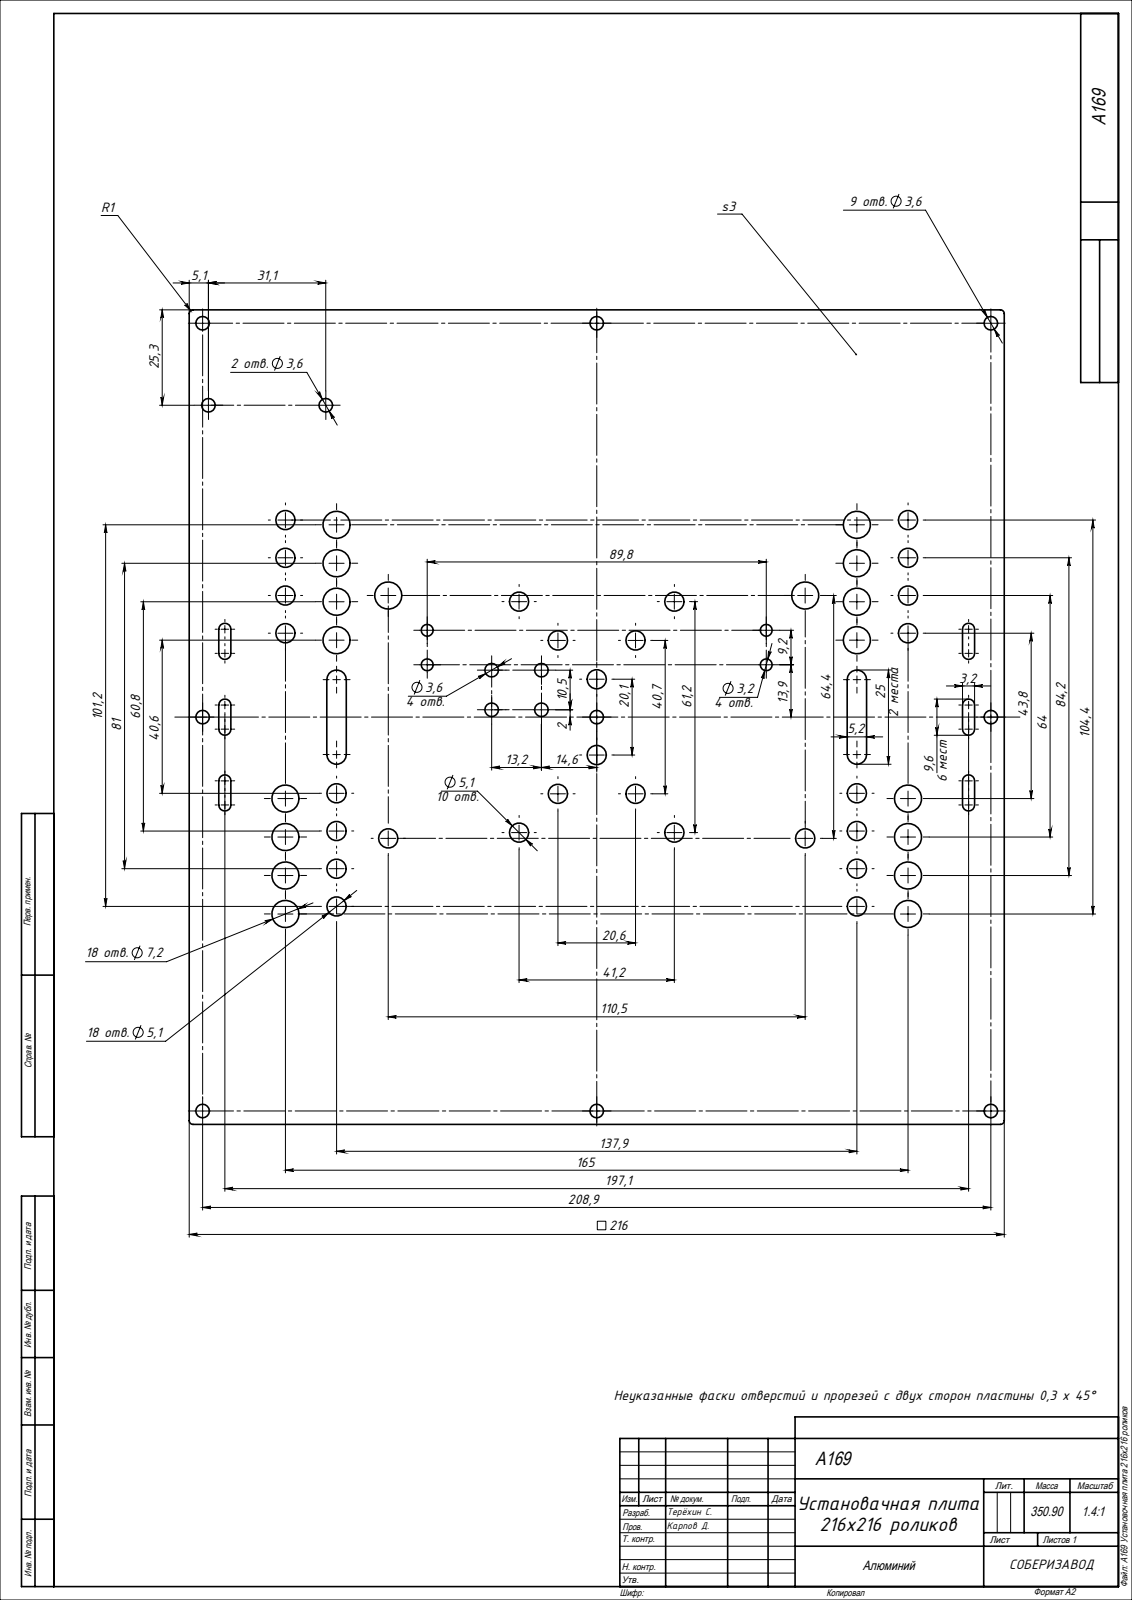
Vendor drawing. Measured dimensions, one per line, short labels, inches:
name: A169 Установочная плита 216х216 роликов
written by: SolidWorks 2019 (AUTOMOTIVE_DESIGN)
unit: in
bodies: 1 solid, 172 faces (22 planar, 150 cylindrical, 0 other)
size: 8.504 × 8.504 × 0.118
volume: 8.192 in³; area: 148.8 in²
holes: 28× ⌀0.201, 18× ⌀0.283, 15× ⌀0.142, 4× ⌀0.124
rounds: 12× R0.063, 4× R0.039, 4× R0.102
face distances: 0.118, 8.504, 1.436, 1.639, 6.865, 7.068, 0.203, 5.43, 0.309, 0.435
hole spacings: 0.394, 0.402, 0.573, 2.907, 0.787, 0.803, 2.514, 2.902
